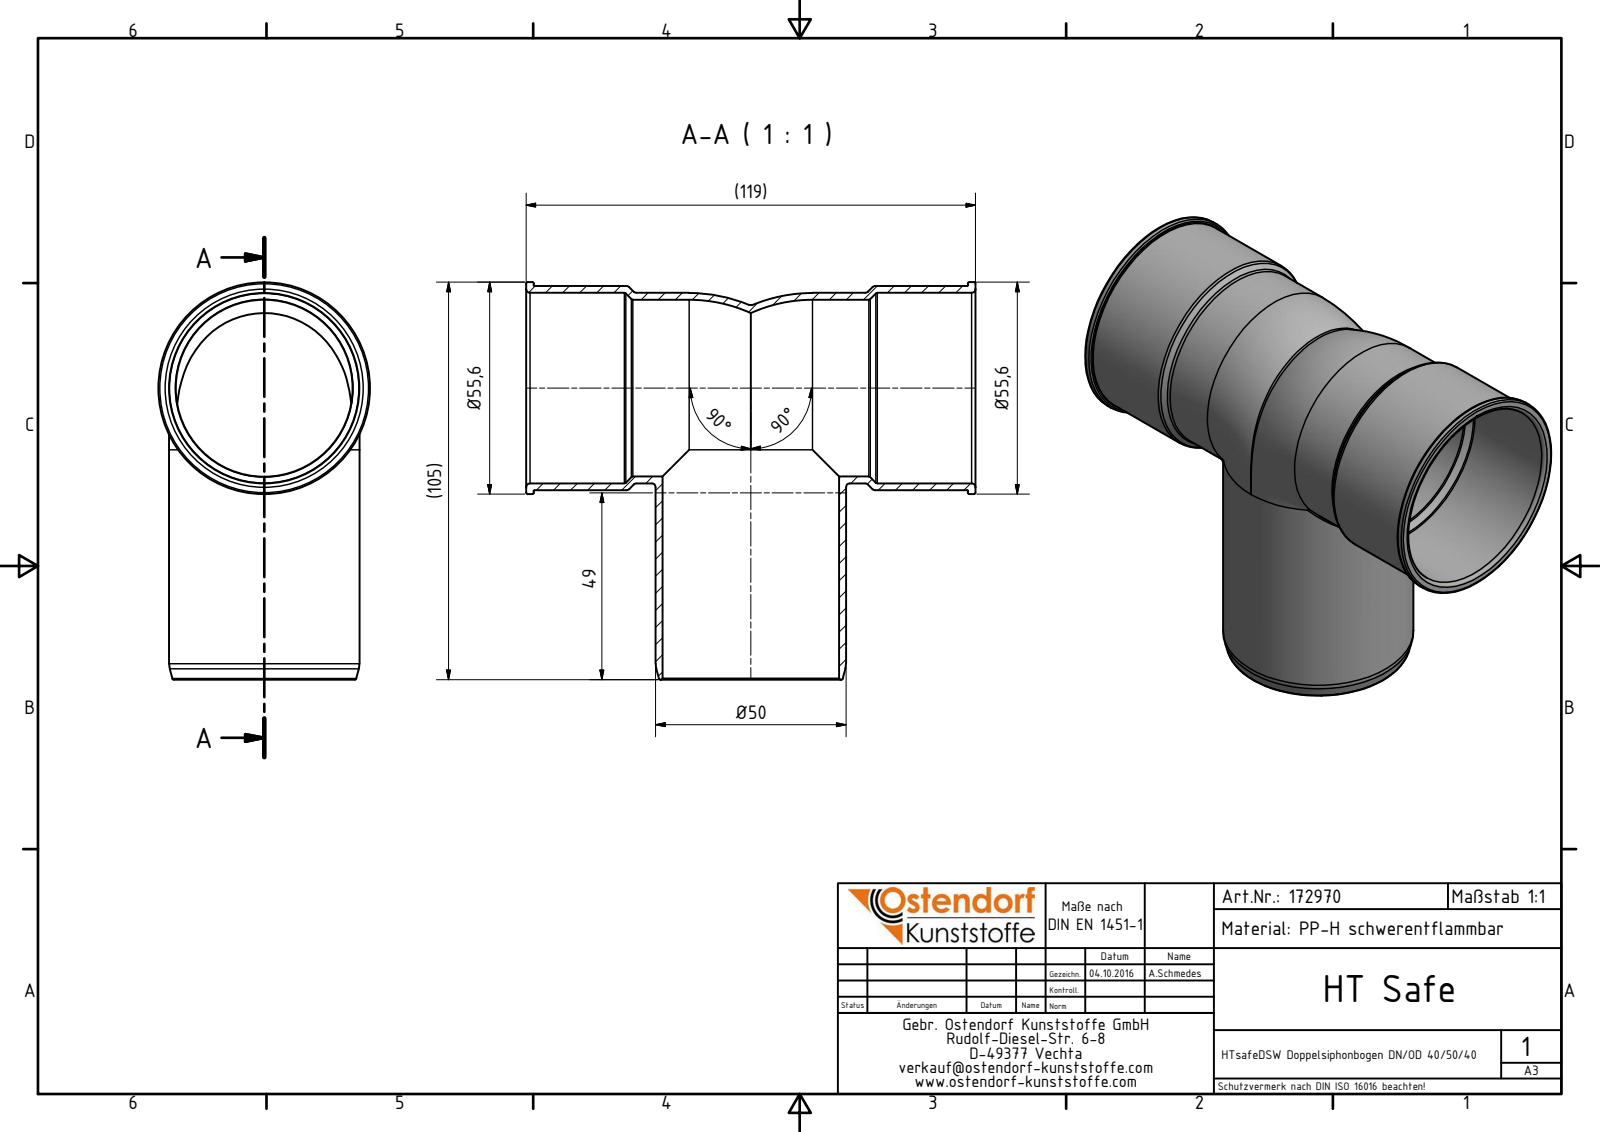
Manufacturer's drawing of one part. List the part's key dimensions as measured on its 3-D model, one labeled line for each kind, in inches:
Part name (STEP PRODUCT): 172970 HTsafeDSW DN_OD 40_50_40
STEP written by: Autodesk Inventor 2016 (AUTOMOTIVE_DESIGN)
Units: inches
Bodies: 1 solid, 48 faces (5 planar, 12 cylindrical, 31 other)
Overall size (bounding box): 4.646 × 4.106 × 2.189
Volume: 2.792 in³ · Surface area: 81.03 in²
Round holes (diameter × count): ⌀1.827 ×2, ⌀1.969 ×1
Round bosses / shafts (diameter × count): ⌀2.189 ×1, ⌀2.11 ×1, ⌀1.969 ×1
Main face-to-face distances: 4.646, 0.079, 4.567, 4.488
